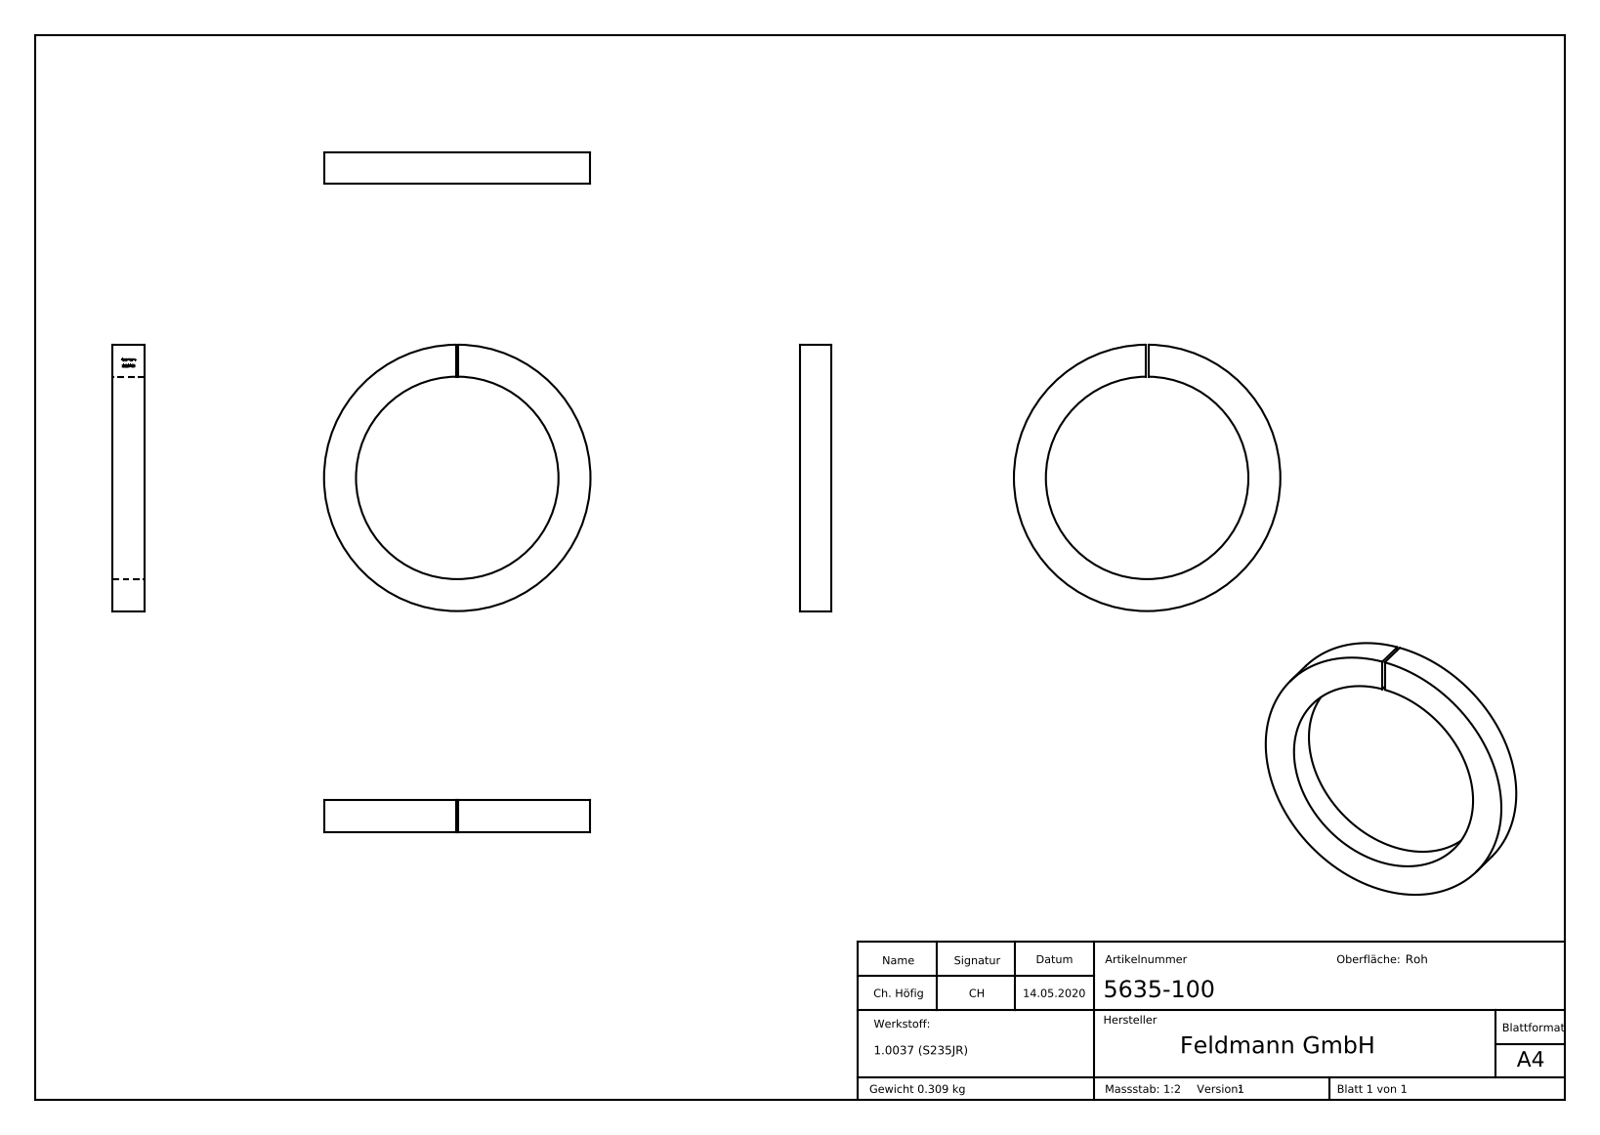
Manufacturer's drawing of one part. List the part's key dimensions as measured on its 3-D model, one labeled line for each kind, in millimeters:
Part name (STEP PRODUCT): 5635-100
STEP written by: SolidWorks 2015 (CONFIG_CONTROL_DESIGN)
Units: millimetres
Bodies: 1 solid, 216 faces (109 planar, 2 cylindrical, 105 other)
Overall size (bounding box): 110 × 110 × 16
Volume: 40 888 mm³ · Surface area: 15 594 mm²
Round holes (diameter × count): ⌀94 ×1
Round bosses / shafts (diameter × count): ⌀110 ×1
Main face-to-face distances: 16, 1, 1.1, 1.78, 0.83, 1.98, 2.12, 2.77, 1.21, 3.33
